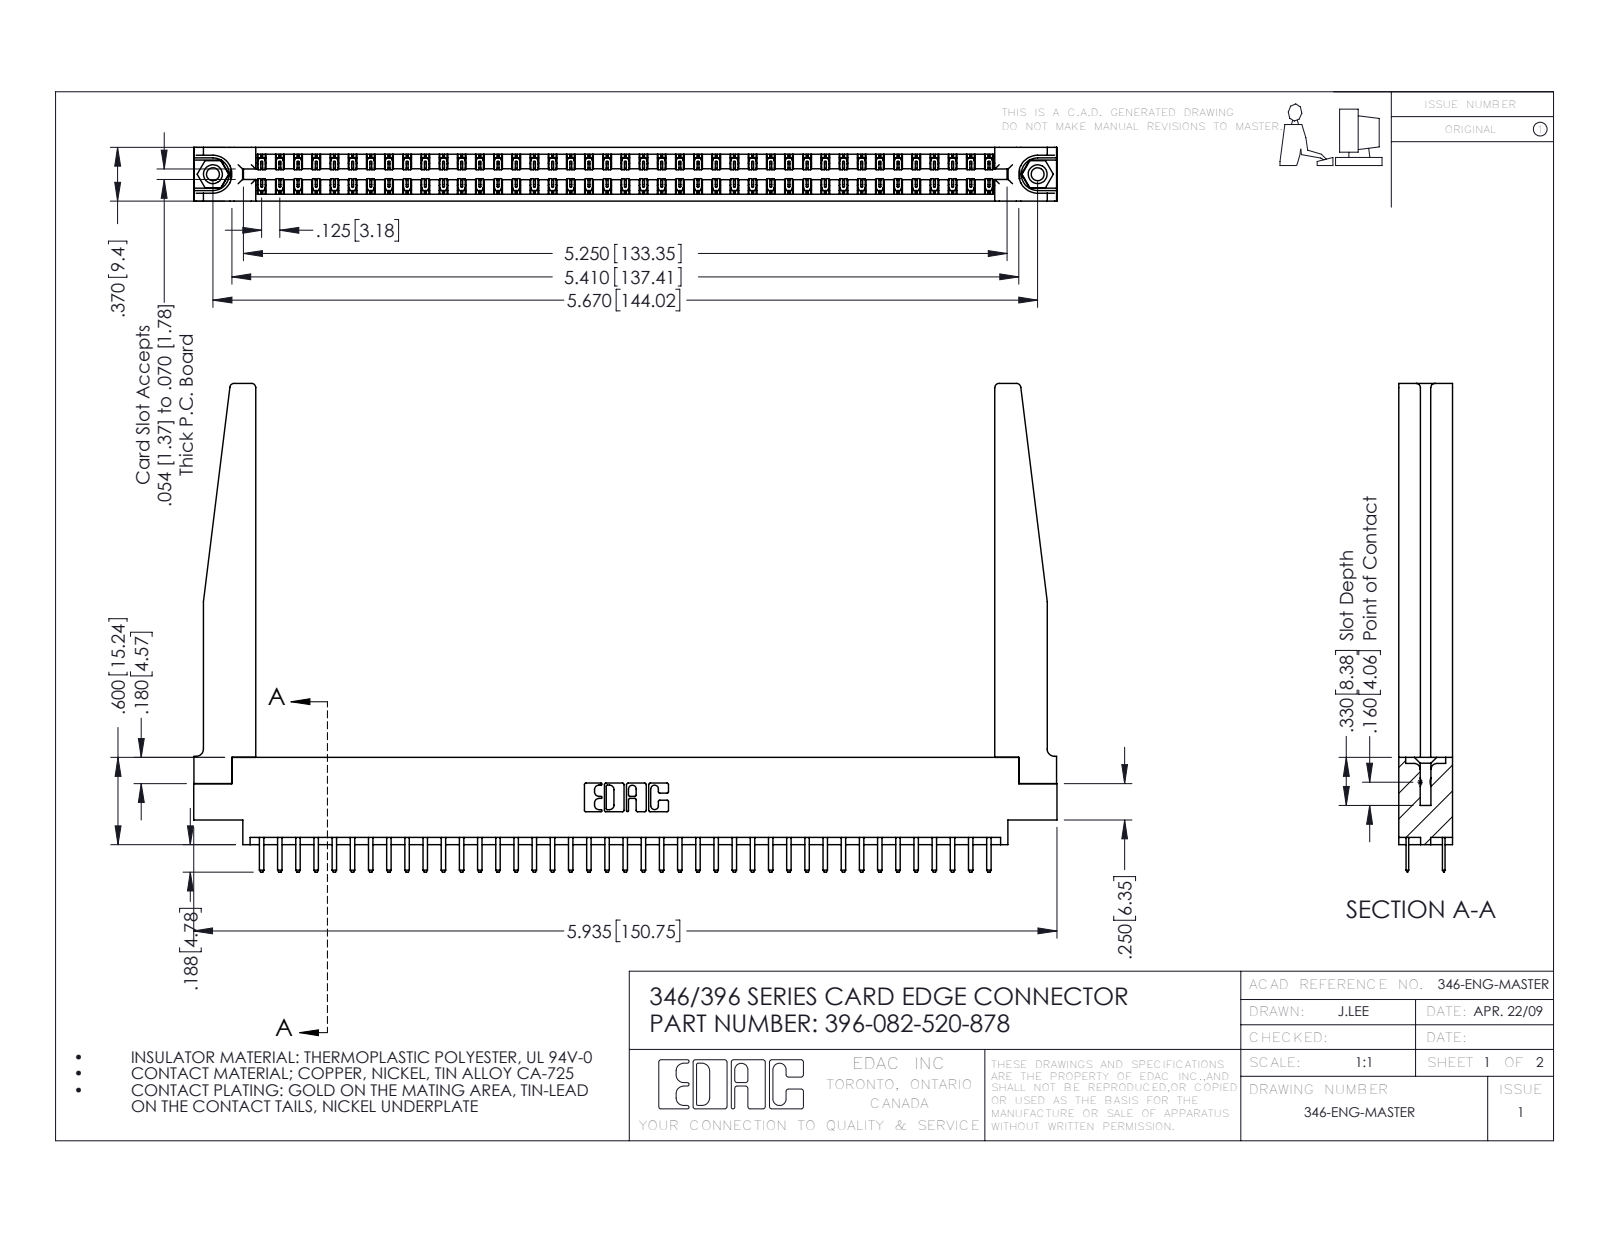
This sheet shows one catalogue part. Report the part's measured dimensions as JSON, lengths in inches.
{"part_name": "346 Part_0.170 Offset - 0.156 Dia-TH; 345-250-001_345-250-001-102; 346-220-078_345-220-078; 345-292-001_345-293-120 (+1 more)", "step_written_by": "SolidWorks 2016 (CONFIG_CONTROL_DESIGN)", "units": "inches", "bodies": {"solids": 87, "faces": 4952, "planar": 3256, "cylindrical": 1644, "other": 52}, "overall_size": [5.935, 3.358, 0.37], "volume_in3": 1.307, "surface_area_in2": 41.15, "round_holes": [[0.089, 2], [0.125, 2], [0.156, 2], [0.064, 1]], "round_bosses_or_shafts": [[0.155, 2]], "partial_cylinders_radius": [[0.006, 123], [0.01, 86], [0.01, 22], [0.03, 8], [0.007, 6], [0.031, 6], [0.026, 3], [0.014, 2]], "face_to_face_distances": [0.37, 0.048, 0.322, 0.25, 0.072, 0.15, 0.148, 0.298, 0.025, 0.275], "hole_center_spacings": [0.246, 5.461, 5.67]}
